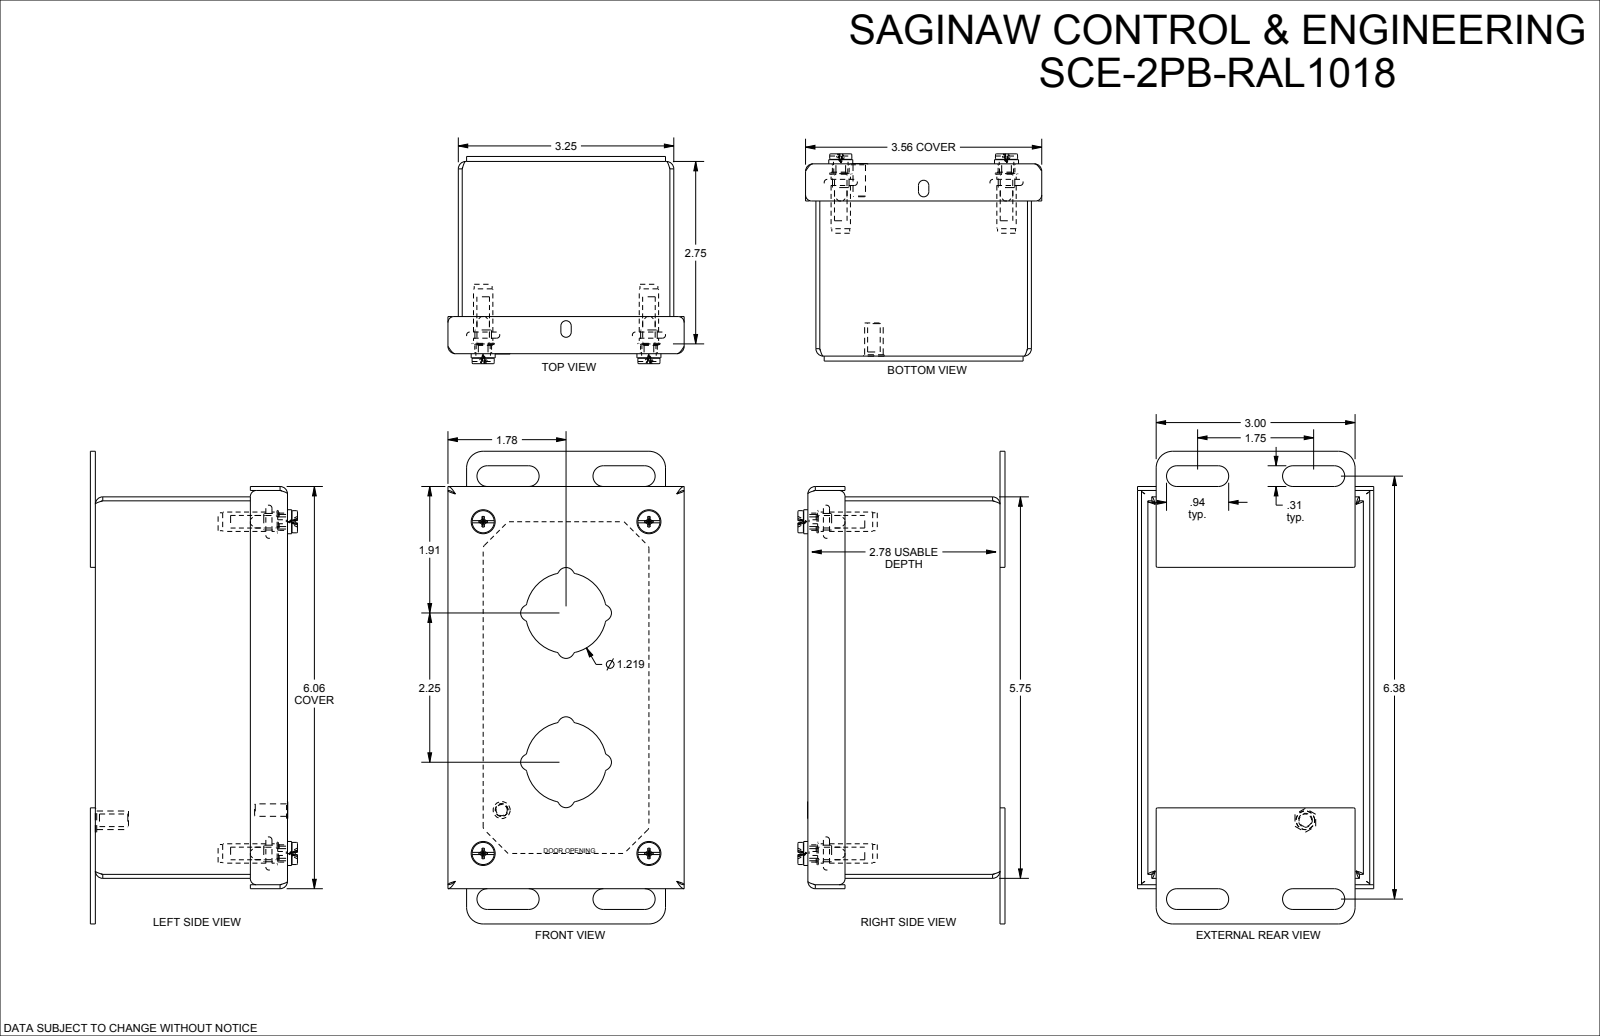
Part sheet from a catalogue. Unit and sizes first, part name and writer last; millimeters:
Units: millimetres
Overall size (bounding box): 181 × 90.5 × 79.3
Round holes (diameter × count): ⌀4.8 ×5, ⌀5.6 ×4, ⌀6.4 ×4, ⌀6.8 ×4, ⌀8.1 ×4
Round bosses / shafts (diameter × count): ⌀4.8 ×5, ⌀11.1 ×4, ⌀9.2 ×4, ⌀8.6 ×4, ⌀8.5 ×4, ⌀7.4 ×4, ⌀6.9 ×4, ⌀6.6 ×4
Partial cylindrical surfaces — rounded edges, fillets, slot ends (radius × count): R1.5 ×20, R1 ×16, R0.4 ×8, R1.6 ×8, R2.9 ×8, R3.2 ×8, R4 ×8, R6.2 ×8
Main face-to-face distances: 1.5, 72.1, 81, 4, 73.6, 70.6, 144.5, 82.6, 79.5, 85
Hole centre spacings: 63.5, 127, 142, 63.5, 127, 142, 125.1, 18
Volume: 120 400 mm³ · Surface area: 157 800 mm²
Bodies: 19 solids, 567 faces (209 planar, 188 cylindrical, 170 other)
Part name (STEP PRODUCT): SCE-2PB-RAL1018
STEP written by: SolidWorks 2021 (AUTOMOTIVE_DESIGN)
